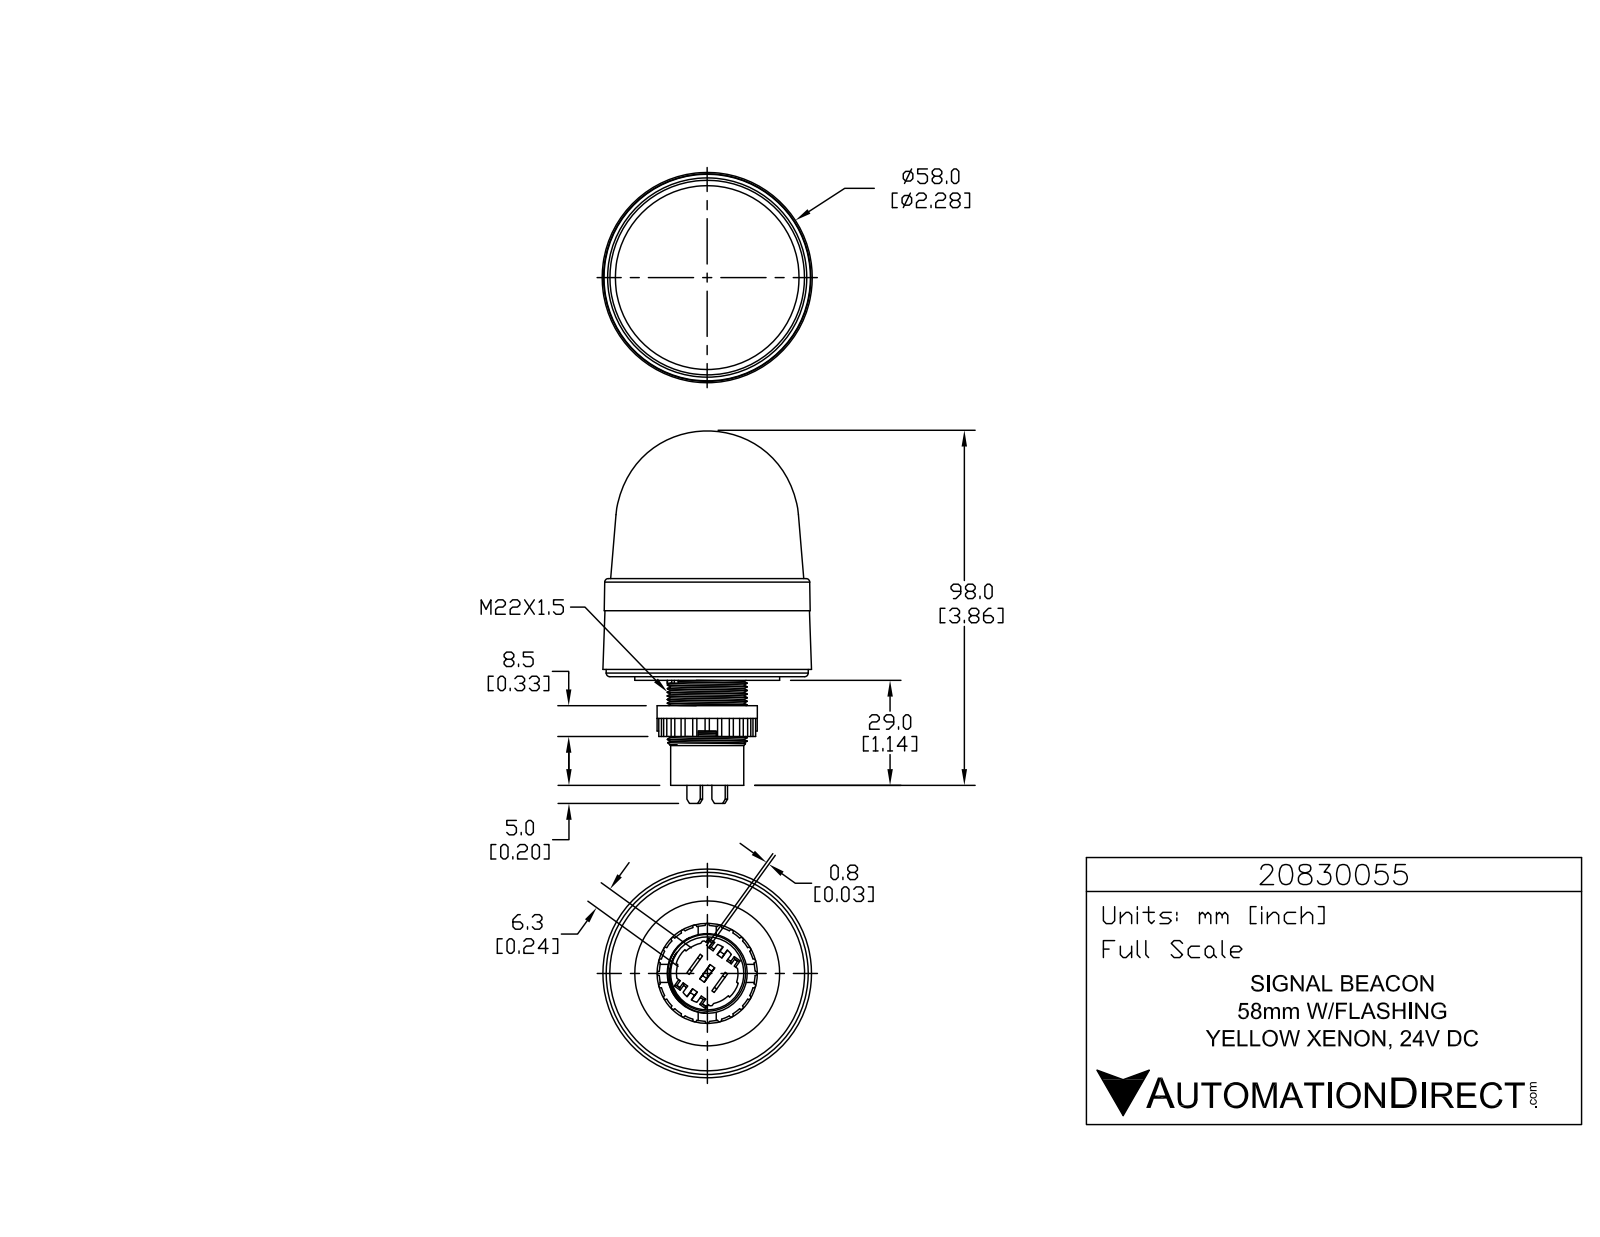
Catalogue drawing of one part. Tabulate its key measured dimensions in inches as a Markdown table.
| quantity | value |
| --- | --- |
| part name | 20830055 |
| STEP written by | SolidWorks 2015 (AUTOMOTIVE_DESIGN) |
| units | inches |
| bodies | 1 solid, 266 faces (119 planar, 120 cylindrical, 27 other) |
| overall size | 4.051 × 2.269 × 2.269 |
| volume | 9.016 in³ |
| surface area | 31.05 in² |
| round holes (diameter × count) | 0.906 × 1 |
| round bosses / shafts (diameter × count) | 2.197 × 1, 1.575 × 1, 1.091 × 1, 0.866 × 1, 0.795 × 1 |
| partial cylindrical surfaces (radius × count) | 0.023 × 24, 0.02 × 2, 0.335 × 1, 0.354 × 1, 0.522 × 1 |
| main face-to-face distances | 0.039, 0.276, 0.118, 1.142, 0.335, 0.315, 1.063, 0.748, 1.024, 0.728 |
